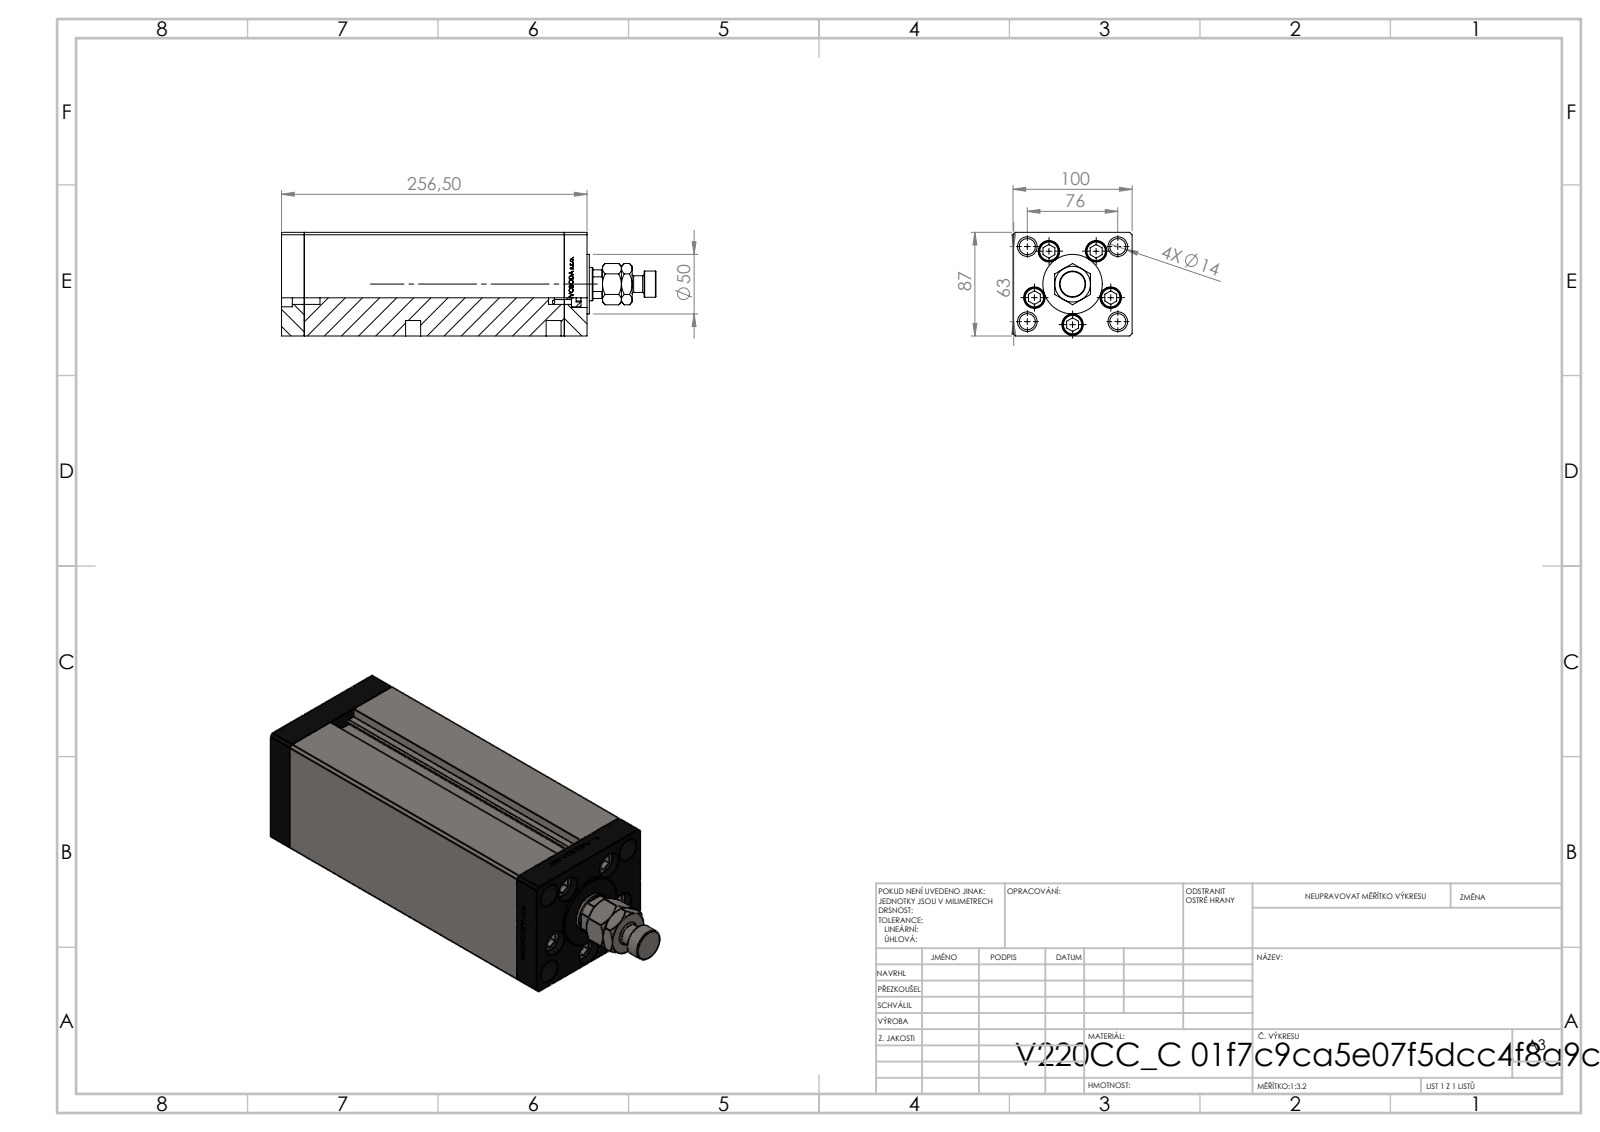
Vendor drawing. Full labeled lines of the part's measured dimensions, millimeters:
Part name (STEP PRODUCT): MFA; ALLEN BOLT; V220C BACK_C; V220C_VC_C (+2 more)
STEP written by: SolidWorks 2019 (CONFIG_CONTROL_DESIGN)
Units: millimetres
Bodies: 14 solids, 1238 faces (564 planar, 180 cylindrical, 494 other)
Overall size (bounding box): 314.5 × 100 × 87
Volume: 1 844 000 mm³ · Surface area: 285 062 mm²
Round holes (diameter × count): ⌀13.5 ×9, ⌀18 ×5, ⌀2 ×4, ⌀12 ×4, ⌀13.16 ×4, ⌀16.5 ×4, ⌀17 ×1, ⌀18.5 ×1, ⌀28 ×1
Round bosses / shafts (diameter × count): ⌀8 ×5, ⌀17 ×4, ⌀50 ×1, ⌀22 ×1, ⌀14 ×1
Partial cylindrical surfaces — rounded edges, fillets, slot ends (radius × count): R0.93 ×2, R13.5 ×1
Main face-to-face distances: 100, 87, 19, 218.5, 237.5, 34.25, 256.5, 222.25, 203.25, 15.25
Hole centre spacings: 34, 49.36, 18.59, 21.03, 38.08, 39.27, 40.83, 43.24
